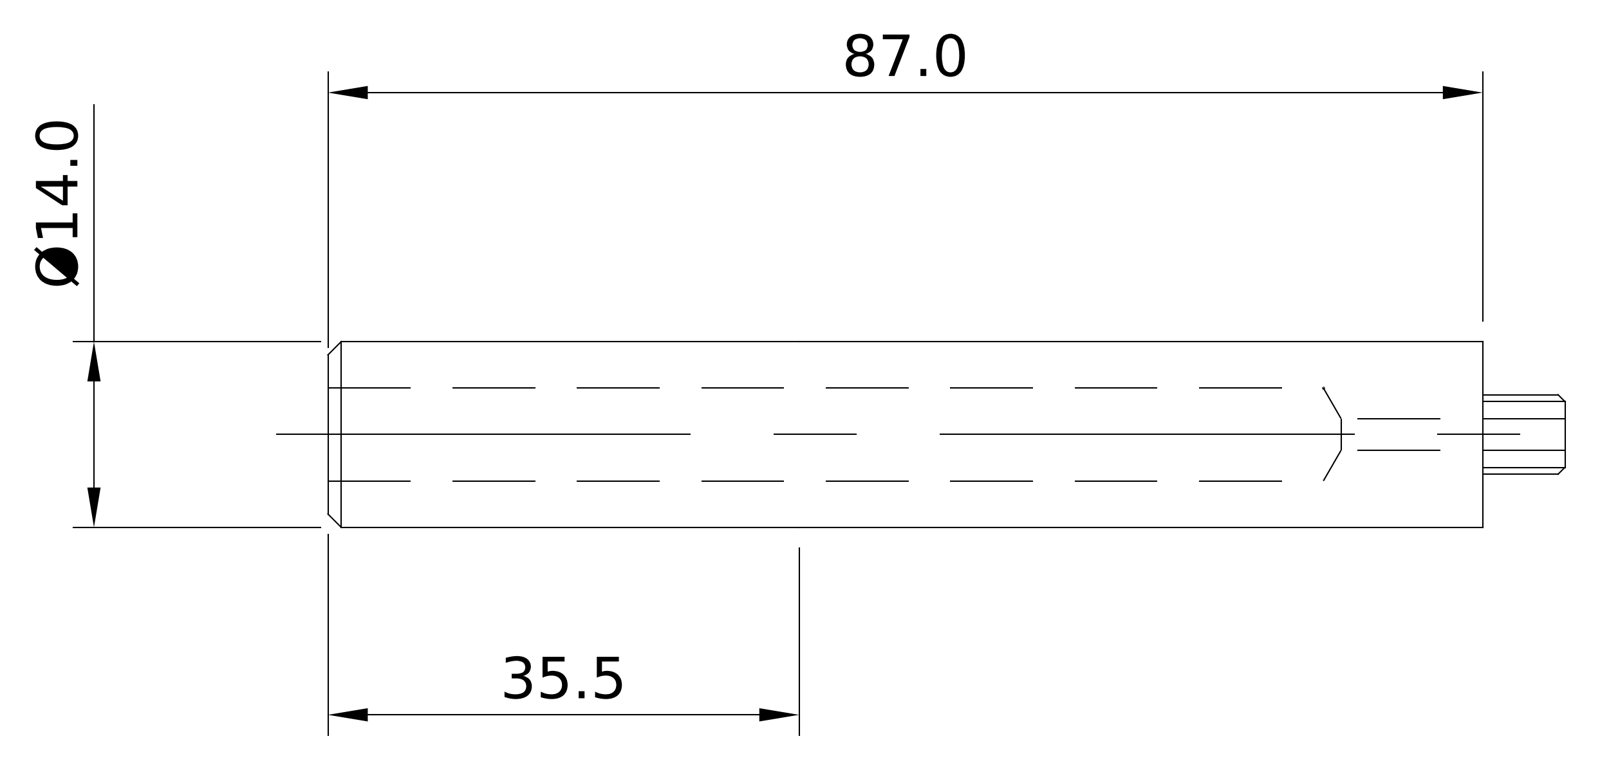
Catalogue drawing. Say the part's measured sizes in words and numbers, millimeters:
Its 3-D file was written by "ACIS (automotive_design)". It is 1 solid with 19 faces: 3 planar, 8 cylindrical and 8 other. Overall it measures 93 by 14 by 14 millimeters. Its volume is 11 898 cubic millimeters and its surface area 5 561 square millimeters. Round holes: 1 of diameter 2, 1 of diameter 5. Round bosses or shafts: 1 of diameter 14, 1 of diameter 6. The main face-to-face distances are 87, 6, 93.
